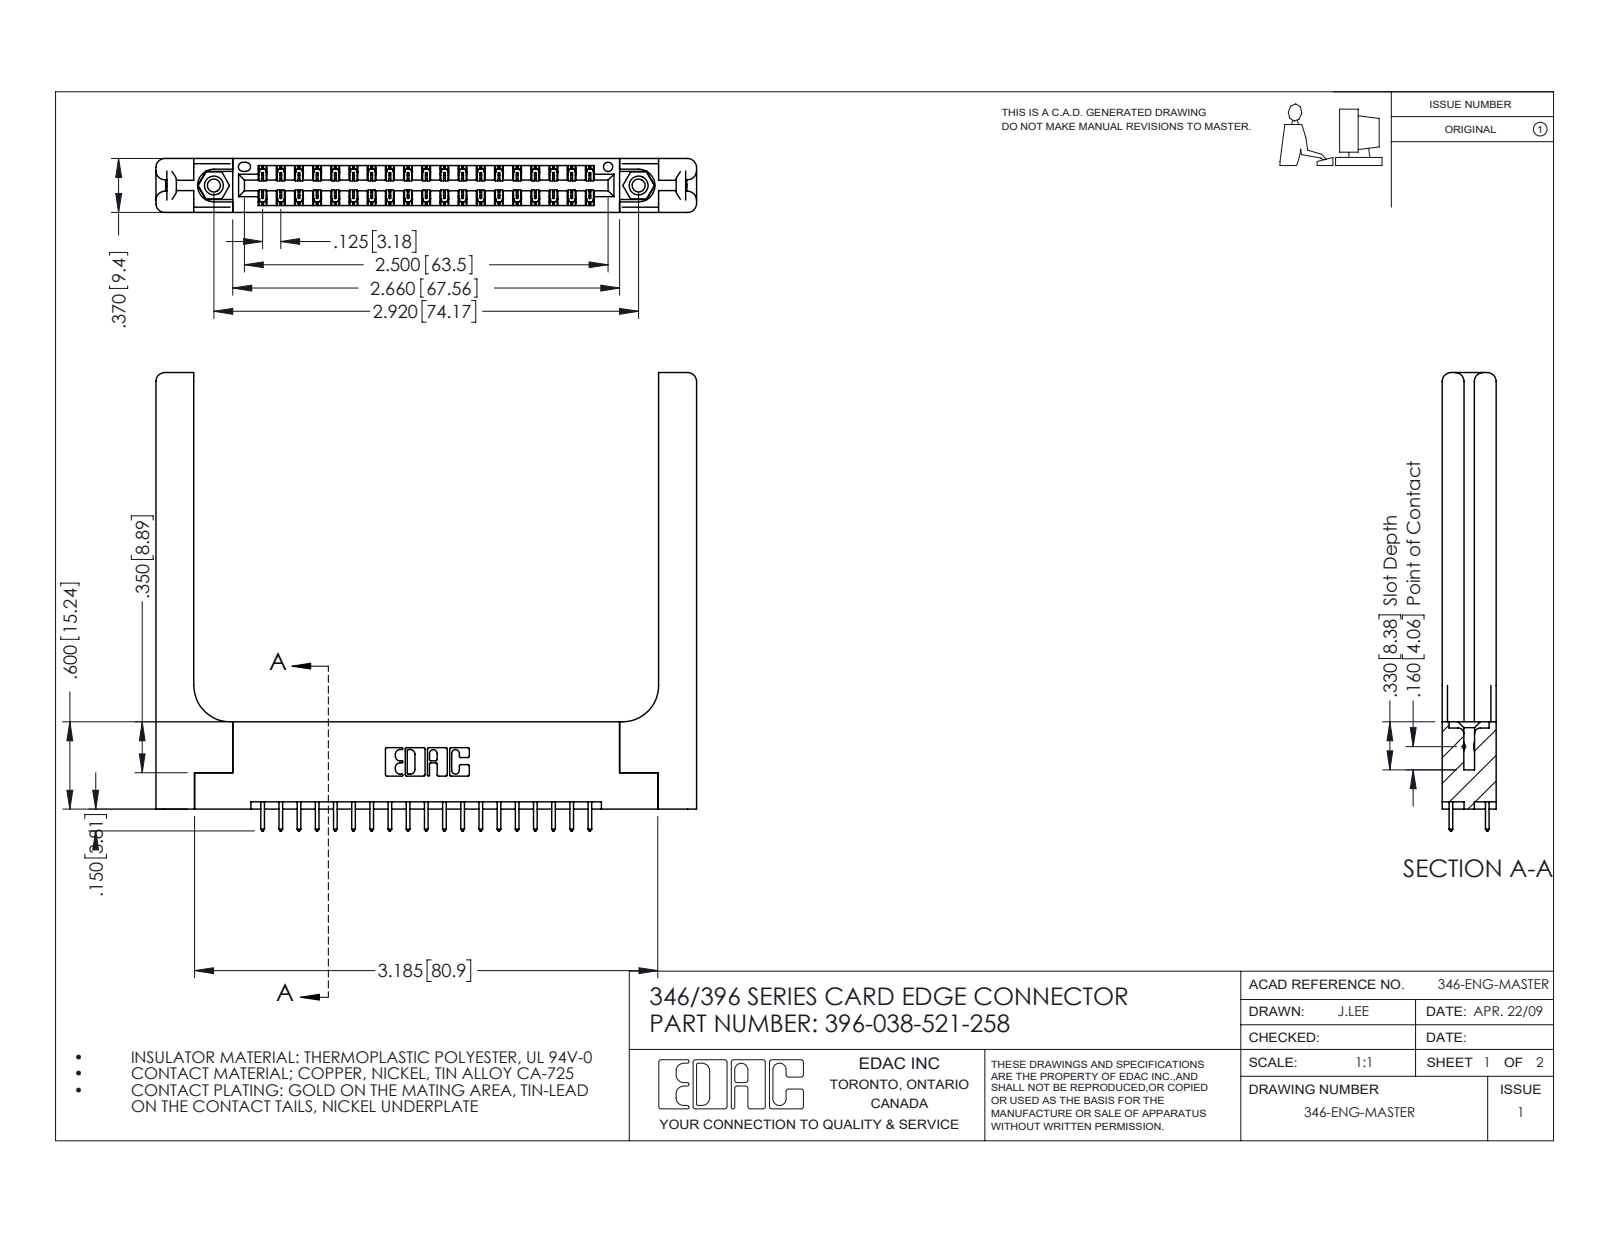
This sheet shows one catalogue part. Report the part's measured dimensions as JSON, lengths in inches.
{"part_name": "346-220-058_345-220-058; 396-038-521-258; 345-292-001_345-293-121; 345-250-001_345-250-001-102 (+1 more)", "step_written_by": "SolidWorks 2016 (CONFIG_CONTROL_DESIGN)", "units": "inches", "bodies": {"solids": 43, "faces": 2354, "planar": 1554, "cylindrical": 740, "other": 60}, "overall_size": [3.716, 3.15, 0.37], "volume_in3": 1.007, "surface_area_in2": 26.18, "round_holes": [[0.089, 2], [0.125, 2], [0.156, 2], [0.064, 1]], "round_bosses_or_shafts": [[0.155, 2]], "partial_cylinders_radius": [[0.006, 57], [0.01, 38], [0.01, 22], [0.06, 16], [0.007, 6], [0.031, 6], [0.026, 3], [0.014, 2]], "face_to_face_distances": [0.37, 0.072, 0.048, 0.322, 0.148, 0.15, 0.25, 0.025, 0.298, 0.077], "hole_center_spacings": [0.246, 2.713, 2.92]}
